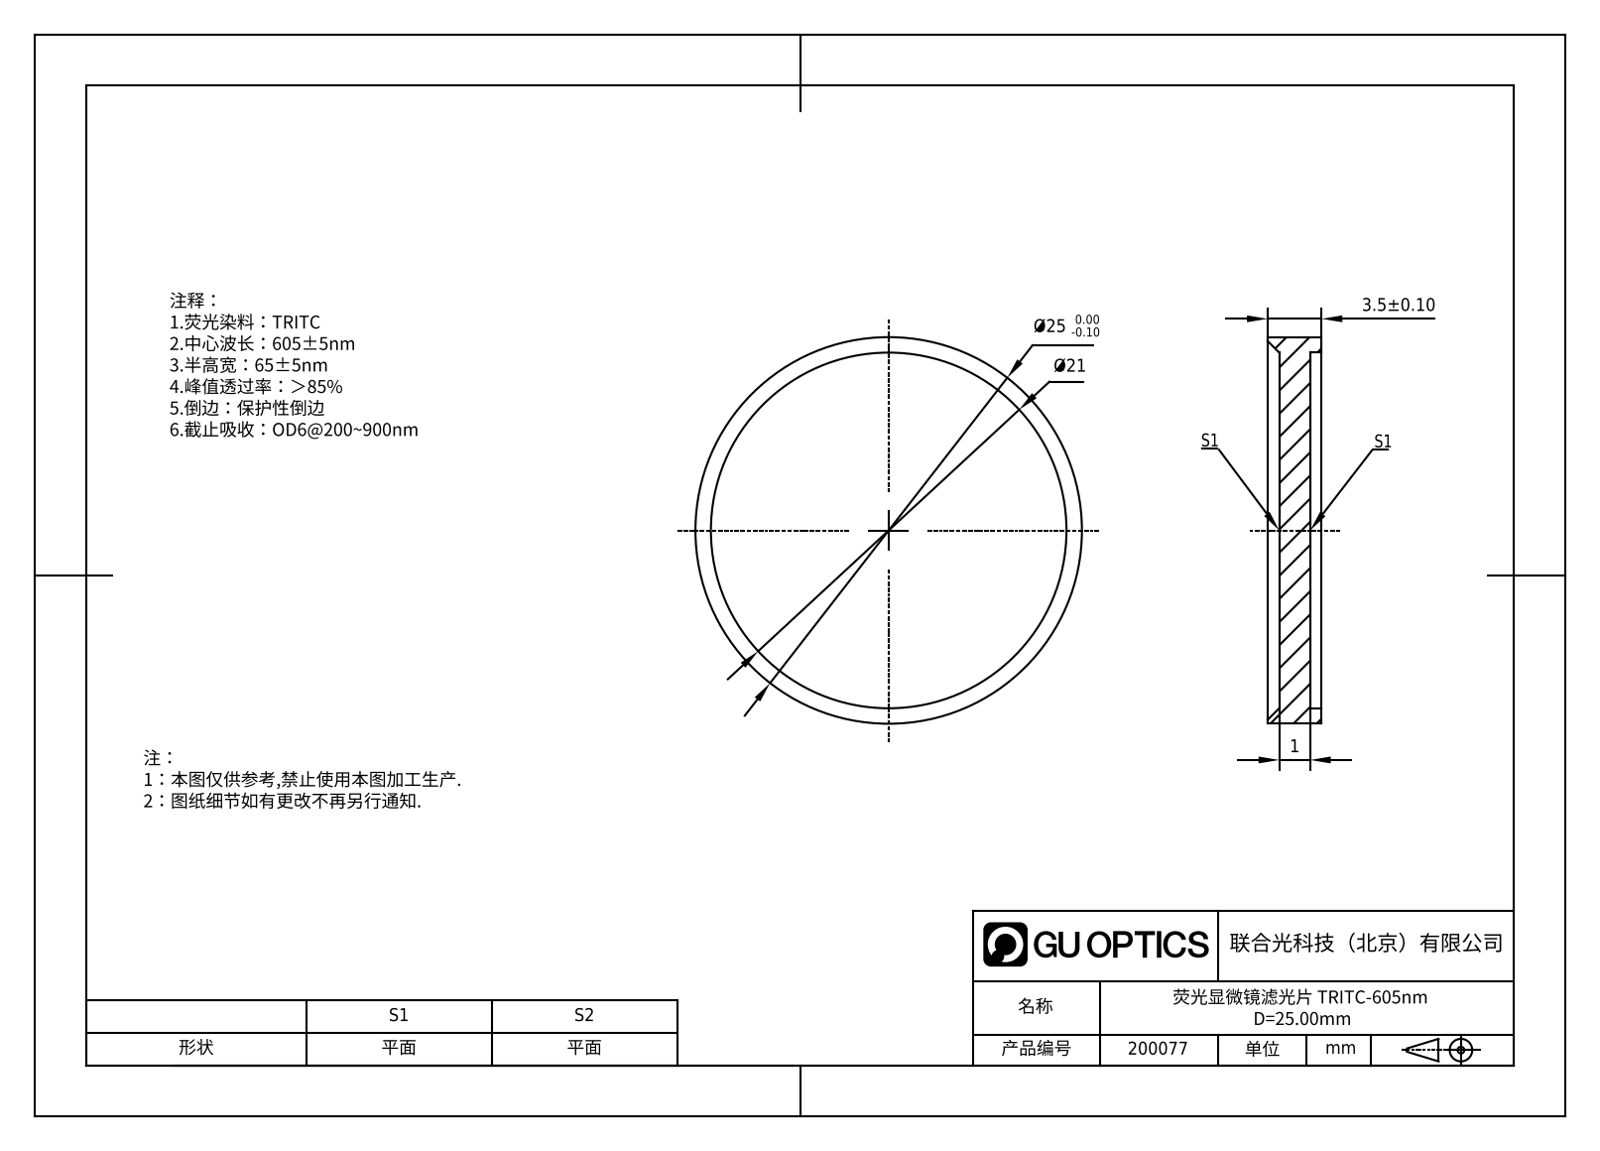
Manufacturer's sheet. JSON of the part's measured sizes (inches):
{"part_name": "GNIF-065-605-D25", "step_written_by": "SolidWorks 2022 (AUTOMOTIVE_DESIGN)", "units": "inches", "bodies": {"solids": 1, "faces": 10, "planar": 4, "cylindrical": 4, "other": 2}, "overall_size": [0.984, 0.984, 0.138], "volume_in3": 0.066, "surface_area_in2": 2.068, "round_holes": [[0.906, 1]], "round_bosses_or_shafts": [[0.984, 1]], "face_to_face_distances": [0.079, 0.03, 0.108, 0.138]}
